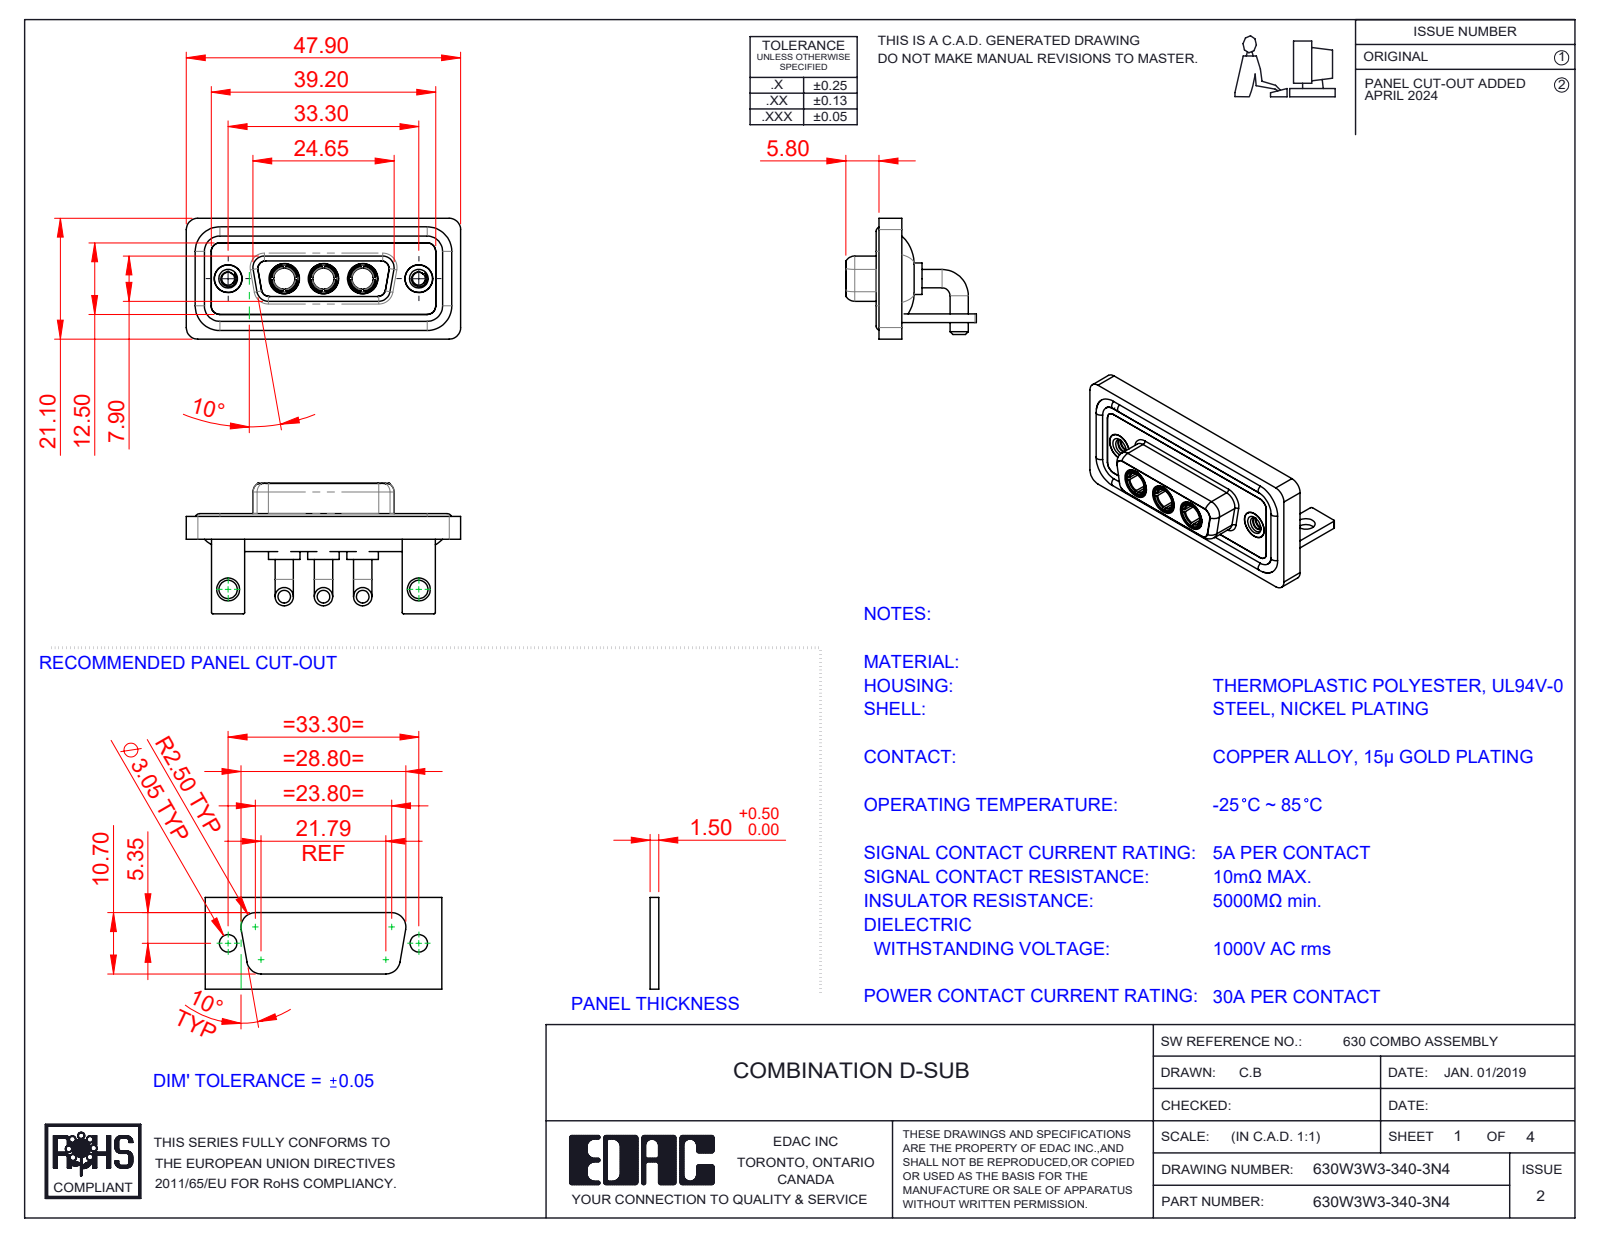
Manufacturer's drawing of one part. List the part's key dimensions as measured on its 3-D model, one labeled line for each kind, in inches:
Part name (STEP PRODUCT): 630W3W3-340-3N4; 630Combo Waterproof Housing_15 Contacts; Power Socket_30A RA; 630Combo Housing_3W3 (+4 more)
STEP written by: SolidWorks 2023 (CONFIG_CONTROL_DESIGN)
Units: inches
Bodies: 15 solids, 668 faces (212 planar, 287 cylindrical, 169 other)
Overall size (bounding box): 1.886 × 0.898 × 0.831
Volume: 0.405 in³ · Surface area: 16.68 in²
Round holes (diameter × count): ⌀0.191 ×5, ⌀0.146 ×3, ⌀0.209 ×3, ⌀0.089 ×2, ⌀0.126 ×2, ⌀0.157 ×2, ⌀0.159 ×2, ⌀0.197 ×2
Round bosses / shafts (diameter × count): ⌀0.126 ×6, ⌀0.063 ×4, ⌀0.217 ×3, ⌀0.205 ×3, ⌀0.195 ×3, ⌀0.187 ×3, ⌀0.148 ×3, ⌀0.195 ×2
Partial cylindrical surfaces — rounded edges, fillets, slot ends (radius × count): R0.079 ×21, R0.059 ×18, R0.01 ×16, R0.053 ×12, R0.063 ×8, R0.02 ×5, R0.024 ×4, R0.026 ×4
Main face-to-face distances: 0.016, 0.114, 0.059, 0.071, 0.146, 0.043, 0.161, 0.063, 0.098, 0.055
Hole centre spacings: 0.27, 0.386, 0.656, 0.925, 1.311, 0.539
